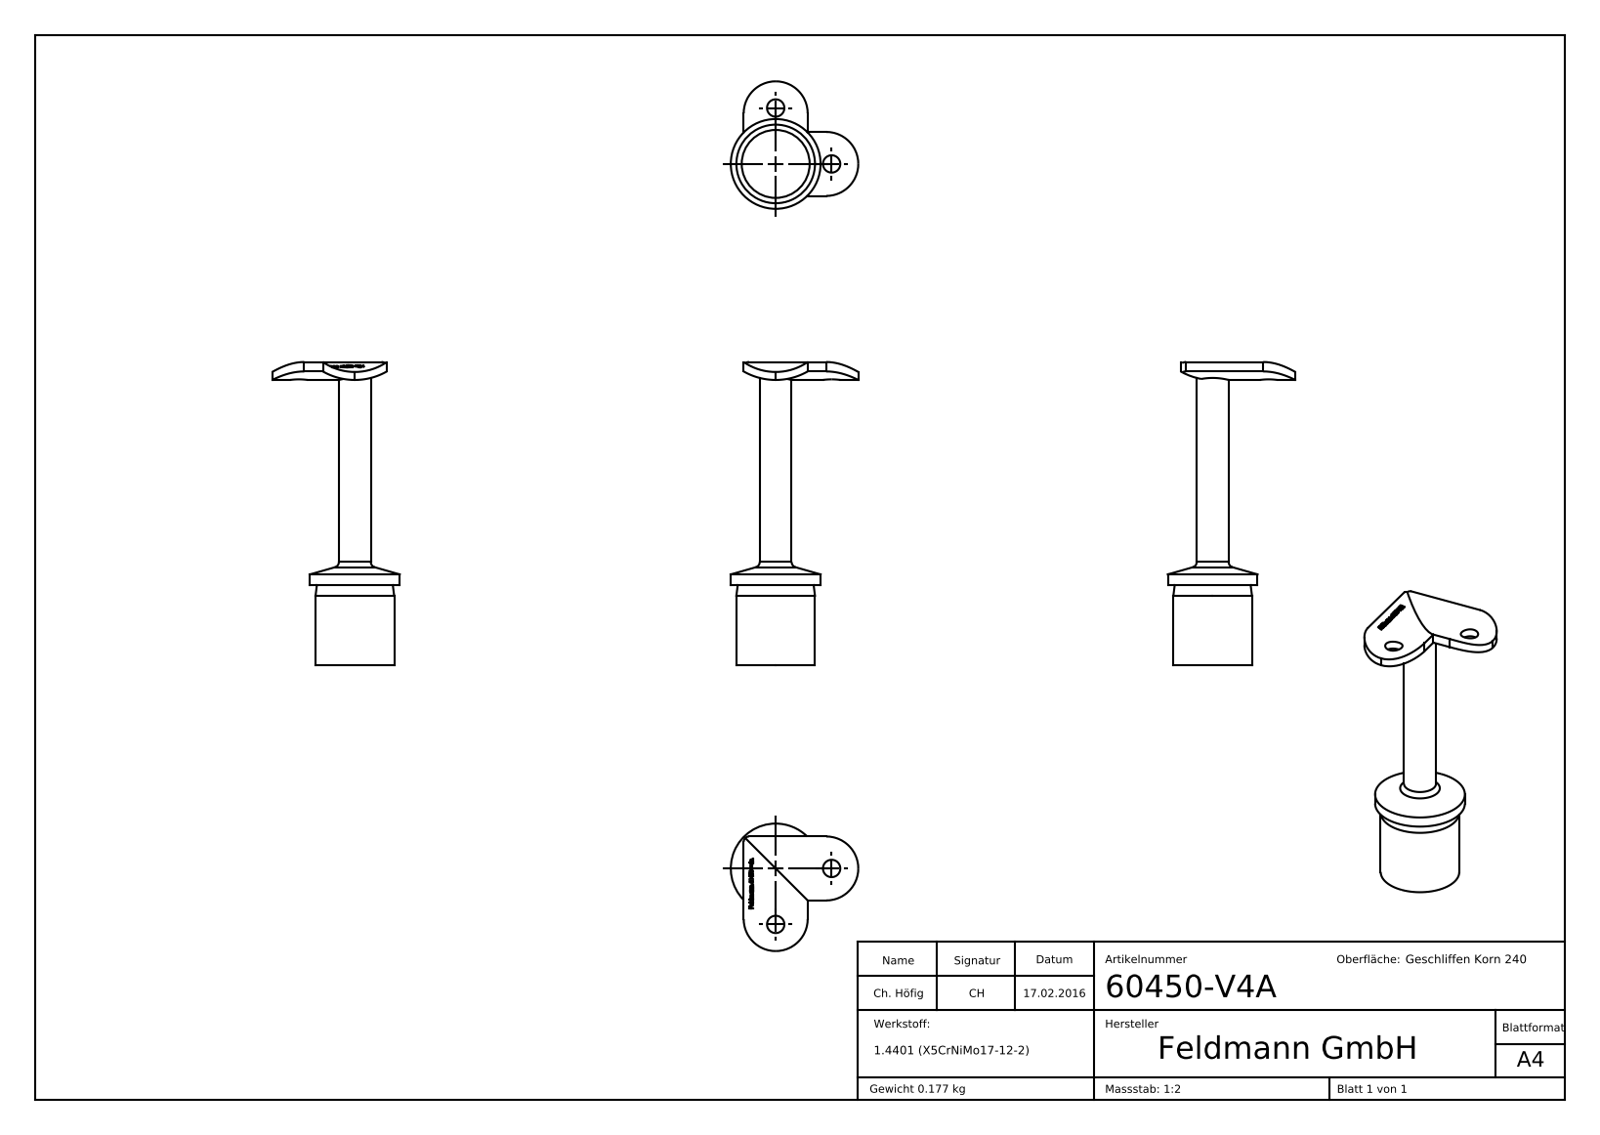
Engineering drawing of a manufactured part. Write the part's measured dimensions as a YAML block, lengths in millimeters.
part_name: "60450-V4A"
step_written_by: "SolidWorks 2015 (CONFIG_CONTROL_DESIGN)"
units: millimeters
bodies: {solids: 1, faces: 254, planar: 135, cylindrical: 30, other: 89}
overall_size: [113.72, 47.85, 47.85]
volume: 22064
surface_area: 13267
round_holes:
  - {diameter: 6.5, count: 2}
  - {diameter: 25.5, count: 1}
round_bosses_or_shafts:
  - {diameter: 33.7, count: 1}
  - {diameter: 29.5, count: 1}
  - {diameter: 12, count: 1}
partial_cylinders:
  - {radius: 12, count: 2}
  - {radius: 21.2, count: 2}
  - {radius: 24.2, count: 2}
  - {radius: 2, count: 1}
face_to_face_distances: [30, 24, 111.72, 81.72, 4.08, 2.18, 21.82, 0.39, 1.26, 2.02]
hole_center_spacings: [21, 29.7]
